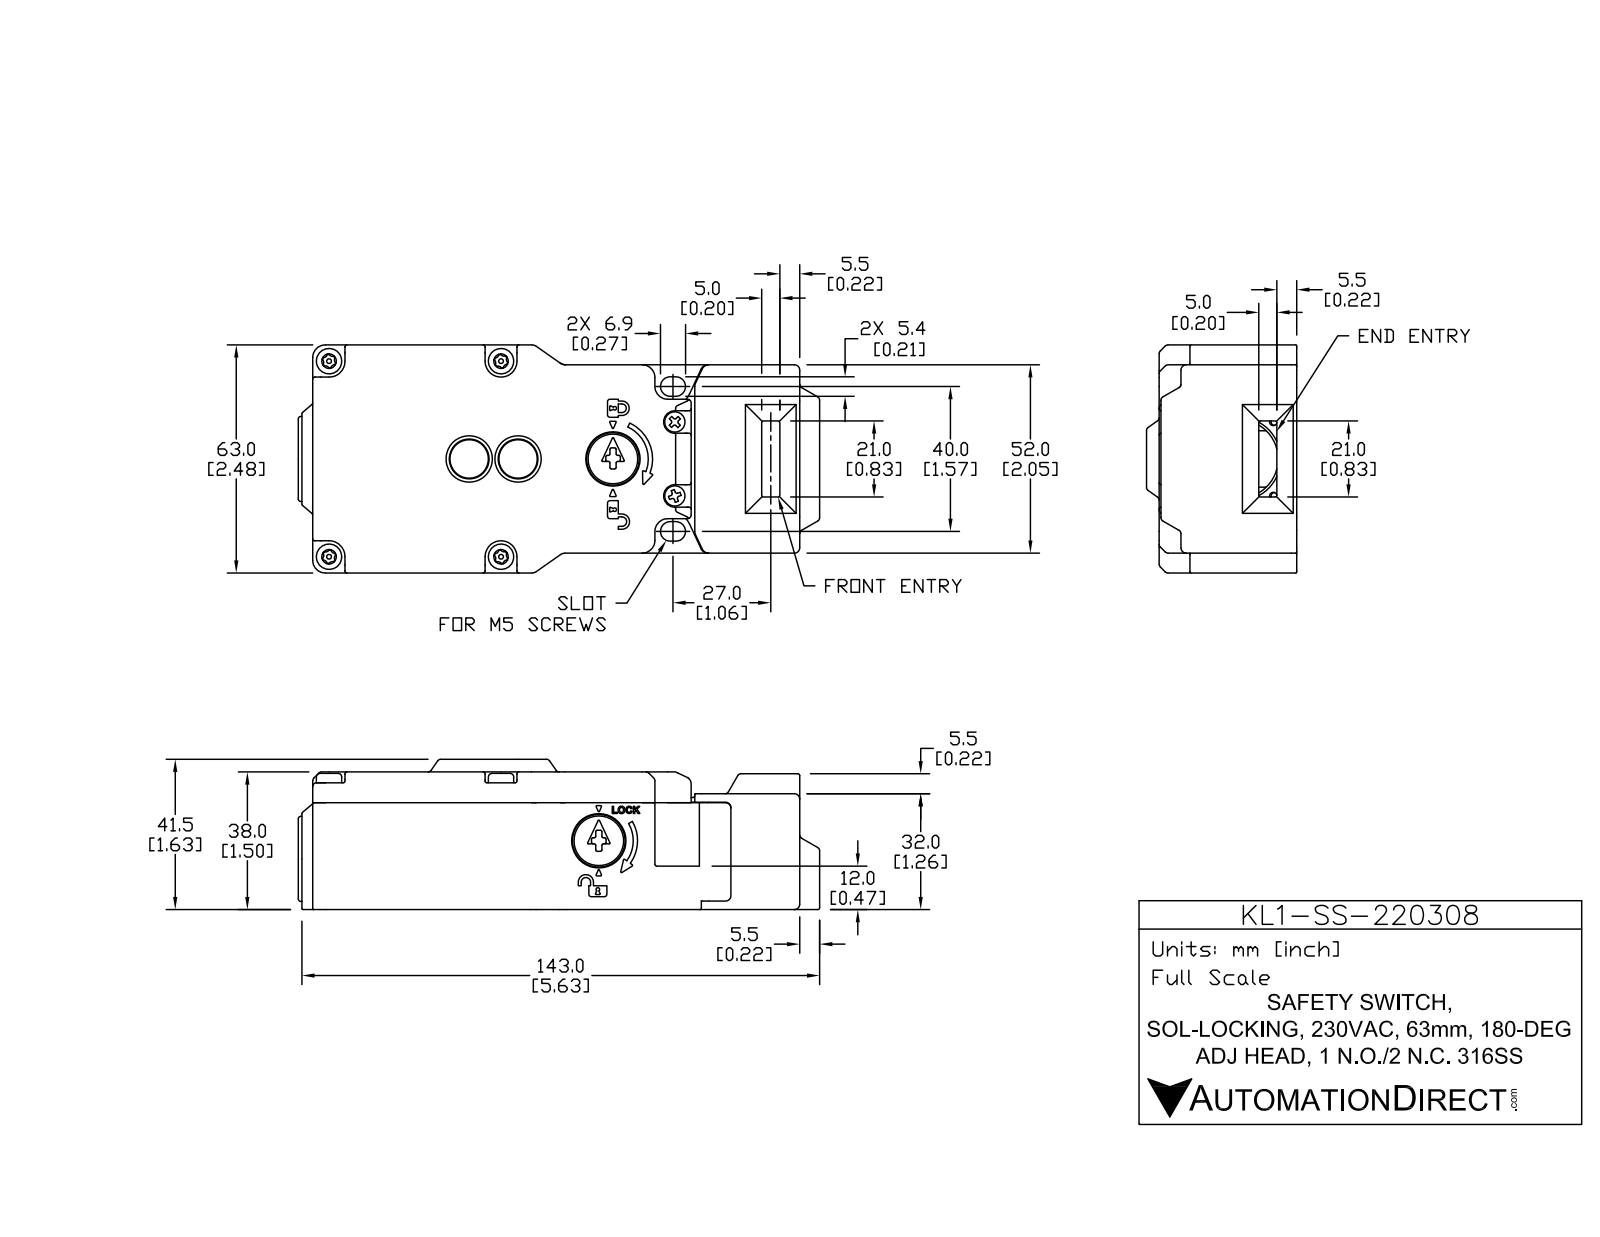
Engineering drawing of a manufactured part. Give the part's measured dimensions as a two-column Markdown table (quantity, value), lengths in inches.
| quantity | value |
| --- | --- |
| part name | KL1-SS-220308 |
| STEP written by | SolidWorks 2017 (AUTOMOTIVE_DESIGN) |
| units | inches |
| bodies | 18 solids, 3047 faces (909 planar, 1225 cylindrical, 913 other) |
| overall size | 5.669 × 2.48 × 1.634 |
| volume | 6.348 in³ |
| surface area | 118.8 in² |
| round holes (diameter × count) | 0.102 × 4, 0.134 × 4, 0.157 × 4, 0.161 × 4, 0.177 × 4, 0.197 × 4, 0.079 × 2, 0.083 × 2, 0.118 × 2, 0.126 × 2, 0.142 × 2, 0.264 × 2 |
| round bosses / shafts (diameter × count) | 0.276 × 4, 0.138 × 4, 0.051 × 4, 0.197 × 3, 0.039 × 3, 0.571 × 2, 0.417 × 2, 0.362 × 2 |
| partial cylindrical surfaces (radius × count) | 0.02 × 348, 0.012 × 126, 0.039 × 106, 0.008 × 30, 0.016 × 24, 0.059 × 16, 0.006 × 14, 0.028 × 12 |
| main face-to-face distances | 0.098, 0.118, 0.217, 1.496, 1.398, 1.402, 1.303, 0.094, 2.264, 2.146 |
| hole center spacings | 0.404, 0.498, 0.515, 0.549, 0.784, 0.803, 1.079, 1.118 |
